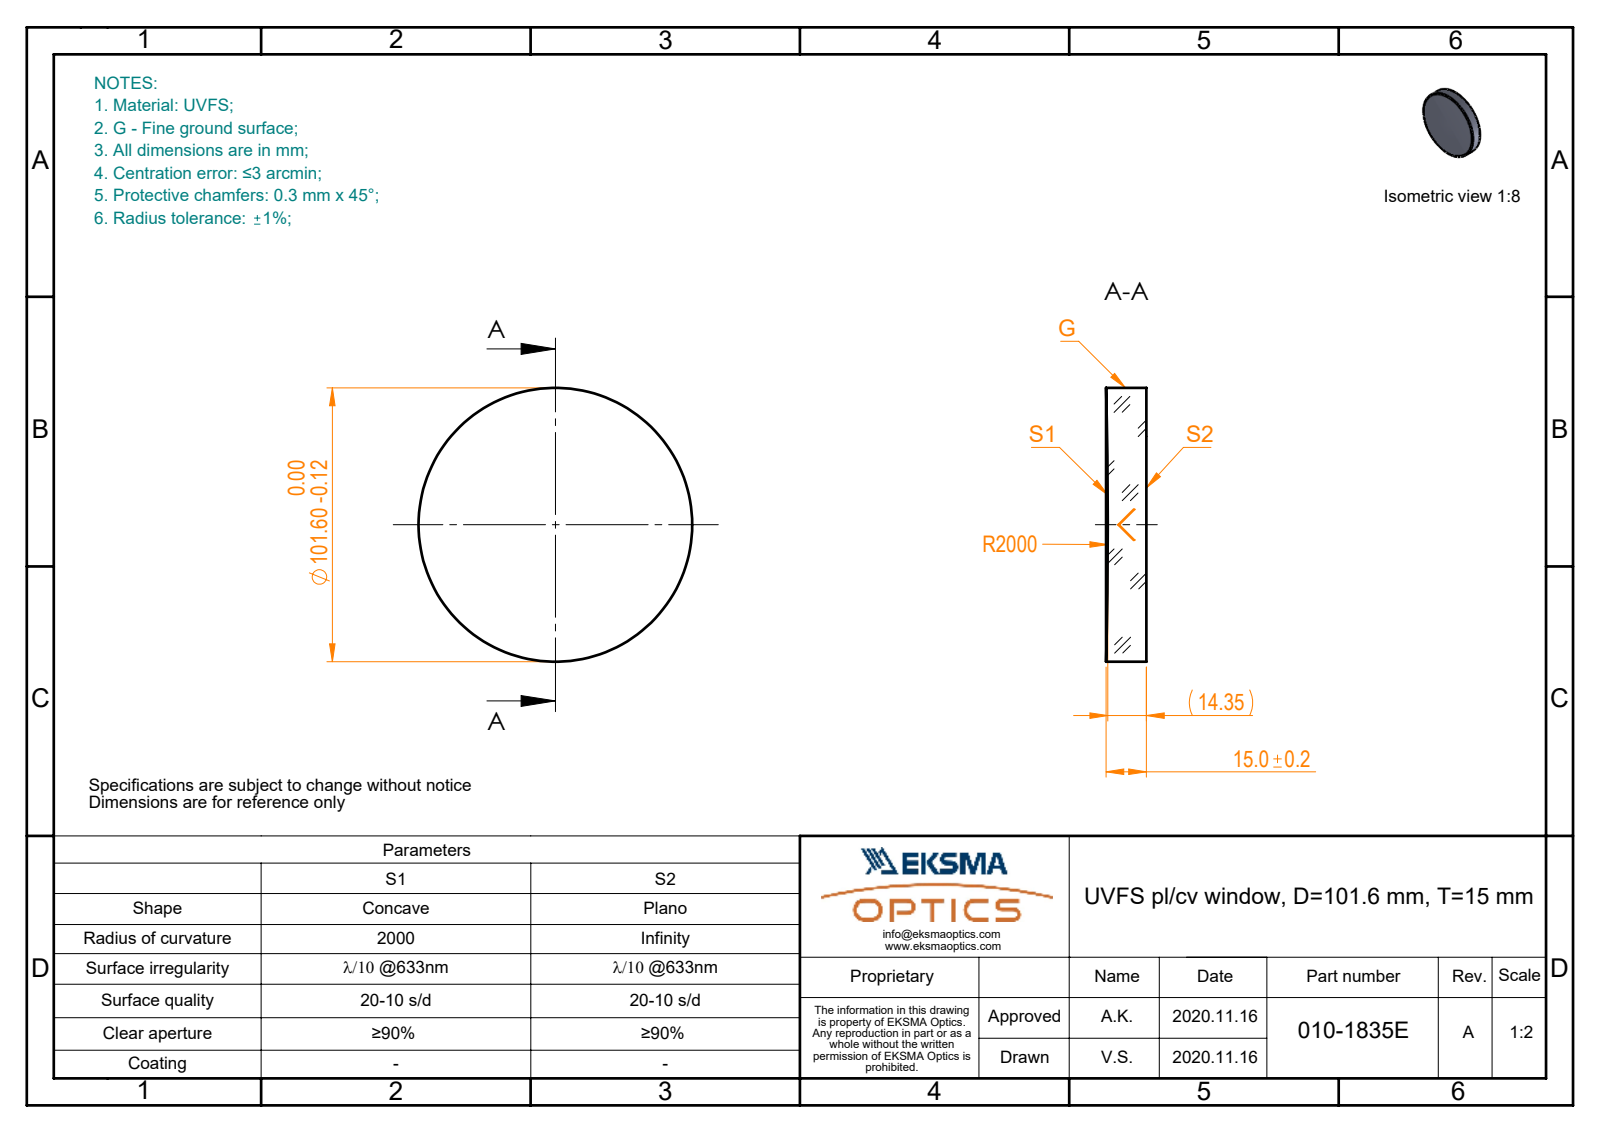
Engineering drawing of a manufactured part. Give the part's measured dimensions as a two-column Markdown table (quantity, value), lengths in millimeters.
| quantity | value |
| --- | --- |
| part name | 010-1835E_UVFS_PCV_window |
| STEP written by | SolidWorks 2019 (CONFIG_CONTROL_DESIGN) |
| units | millimeters |
| bodies | 1 solid, 5 faces (1 planar, 2 cylindrical, 2 other) |
| overall size | 101.6 × 101.6 × 15 |
| volume | 118 994 mm³ |
| surface area | 21 004 mm² |
| round bosses / shafts (diameter × count) | 101.6 × 1 |
